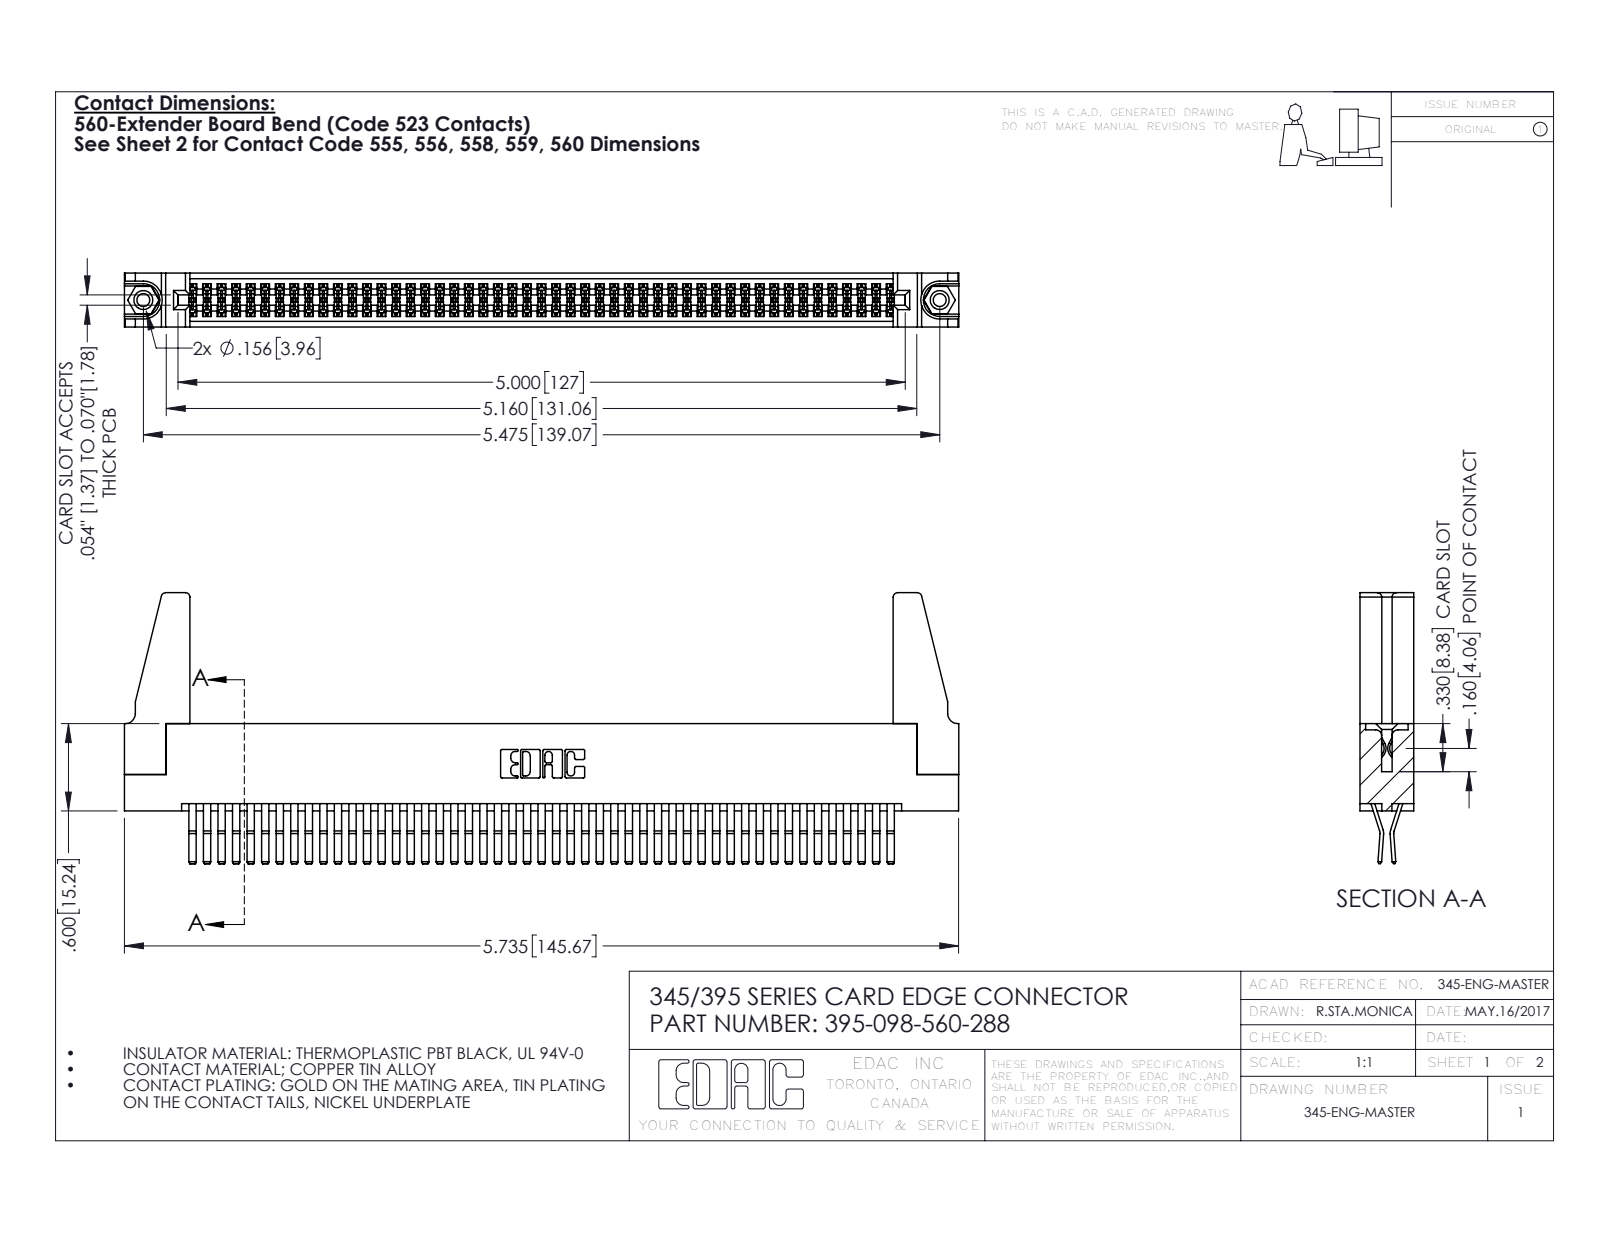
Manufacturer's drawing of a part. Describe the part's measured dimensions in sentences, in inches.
The part is named "345-220-078_345-220-088; 395-098-560-288; 345-292-001_560 Tail; 345-250-001_345-250-001-102 (+1 more)". Its 3-D file was written by "SolidWorks 2016 (CONFIG_CONTROL_DESIGN)". It is 103 solids with 5346 faces: 3386 planar, 1944 cylindrical and 16 other. Overall it measures 5.736 by 1.862 by 0.37 inches. Its volume is 1.105 cubic inches and its surface area 41.66 square inches. Round holes: 2 of diameter 0.089, 2 of diameter 0.125, 2 of diameter 0.156, 1 of diameter 0.064. Round bosses or shafts: 2 of diameter 0.155. Partial cylindrical surfaces (rounded edges, fillets, slot ends): 147 of radius 0.006, 22 of radius 0.01, 8 of radius 0.03, 6 of radius 0.007, 6 of radius 0.031, 3 of radius 0.026, 2 of radius 0.01, 2 of radius 0.014. The main face-to-face distances are 0.072, 0.298, 0.025, 0.37, 0.2, 0.098, 0.272, 0.225, 0.175, 0.149. The hole center spacings are 0.27, 5.239, 5.475.
